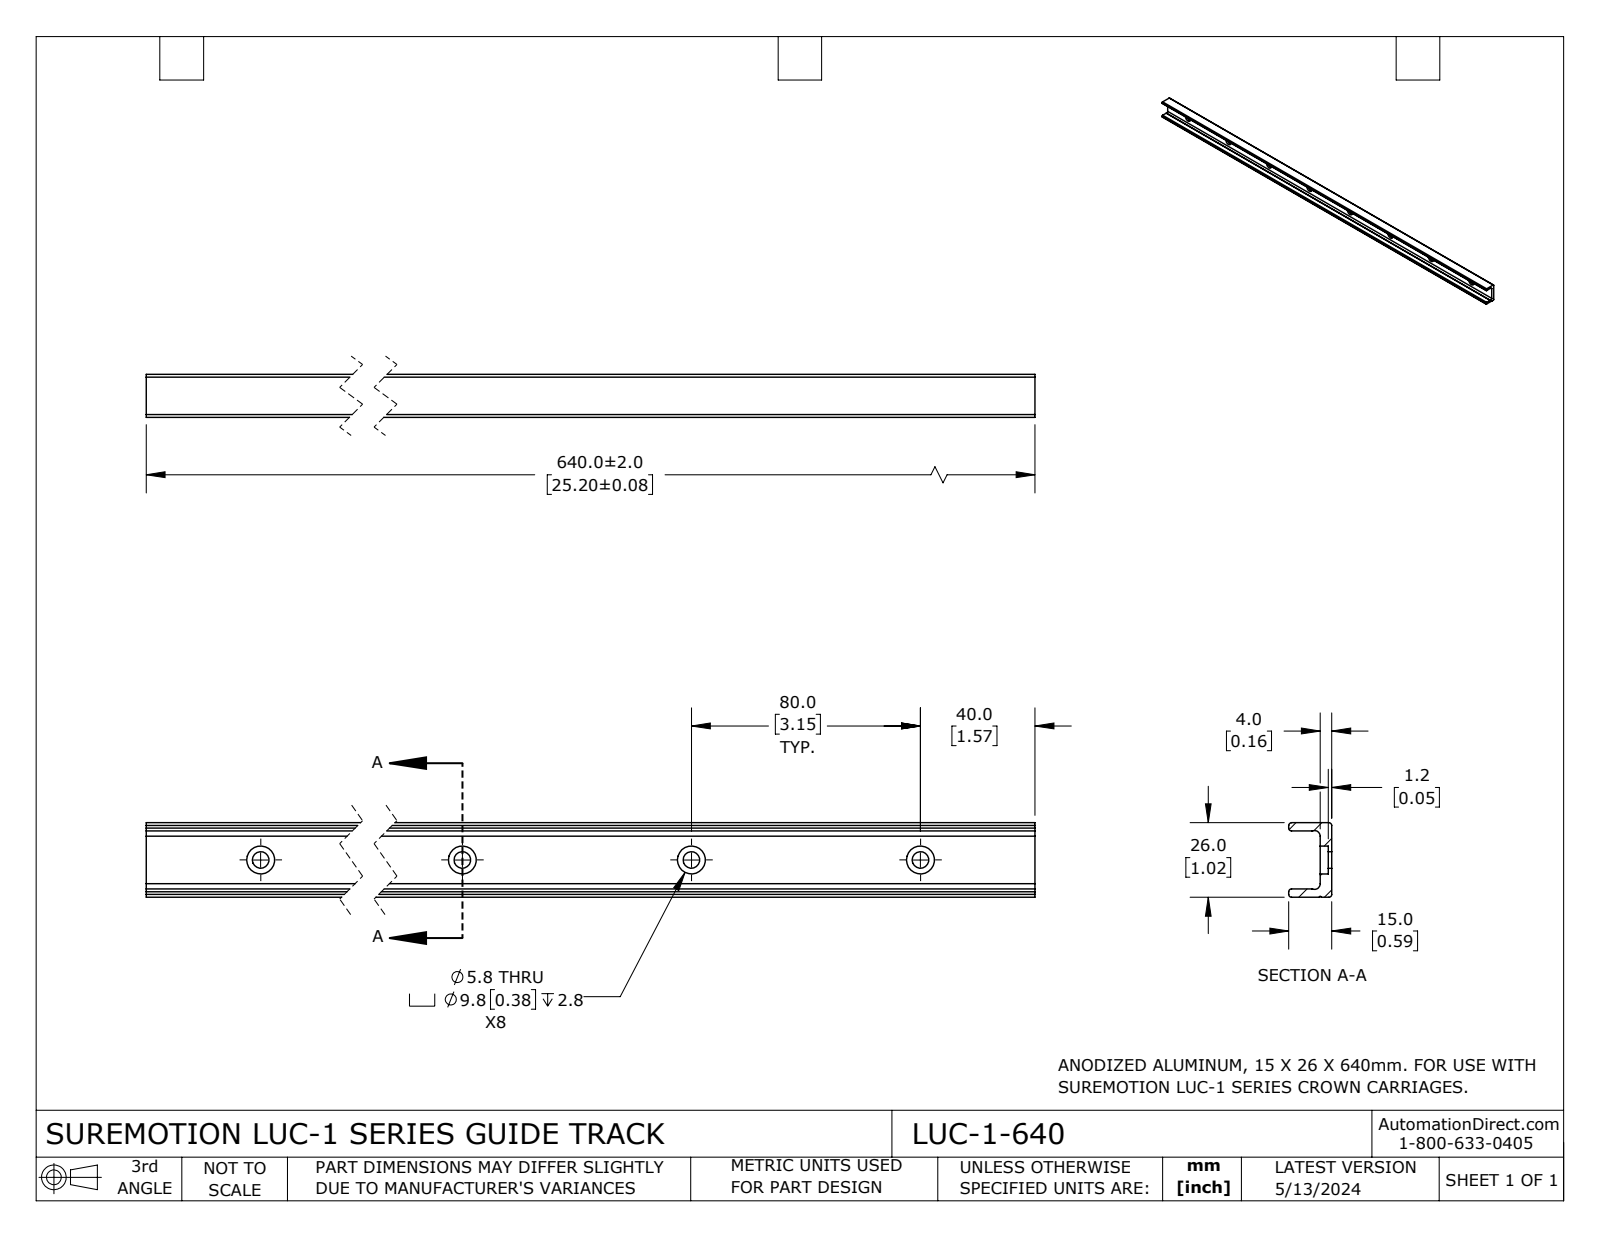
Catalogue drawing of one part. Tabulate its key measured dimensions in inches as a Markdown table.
| quantity | value |
| --- | --- |
| part name | LUC-1-640 |
| STEP written by | SolidWorks 2023 (CONFIG_CONTROL_DESIGN) |
| units | inches |
| bodies | 1 solid, 62 faces (19 planar, 43 cylindrical, 0 other) |
| overall size | 25.197 × 1.024 × 0.591 |
| volume | 6.424 in³ |
| surface area | 100.9 in² |
| round holes (diameter × count) | 0.228 × 8, 0.384 × 8 |
| partial cylindrical surfaces (radius × count) | 0.039 × 8, 0.078 × 2, 0.013 × 1 |
| main face-to-face distances | 0.158, 0.114, 0.91, 1.024, 0.796, 0.591, 0.433, 0.048, 0.11, 0.544 |
| hole center spacings | 3.15, 6.299, 9.449, 12.598, 15.748, 18.898, 22.047 |
